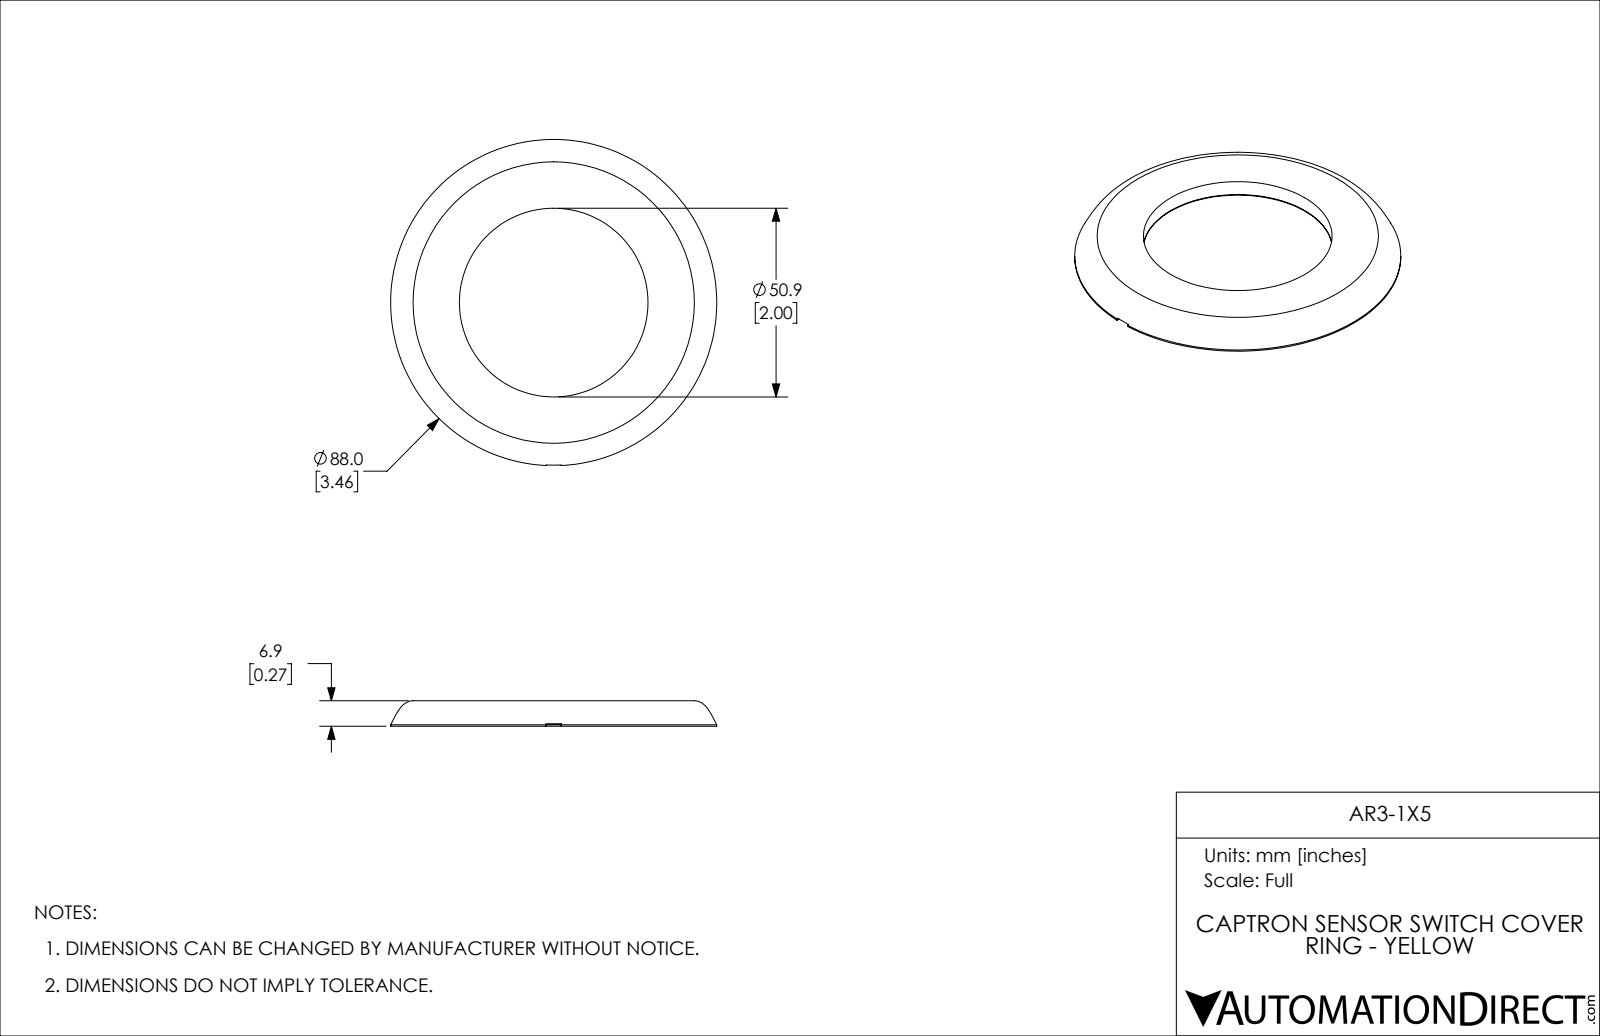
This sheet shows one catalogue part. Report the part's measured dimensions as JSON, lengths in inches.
{"part_name": "AR3-1X5", "step_written_by": "SolidWorks 2019 (CONFIG_CONTROL_DESIGN)", "units": "inches", "bodies": {"solids": 1, "faces": 54, "planar": 12, "cylindrical": 4, "other": 38}, "overall_size": [3.465, 3.463, 0.272], "volume_in3": 0.52, "surface_area_in2": 17.43, "round_holes": [[0.197, 1]], "round_bosses_or_shafts": [[2.177, 1]], "face_to_face_distances": [0.063, 0.122, 0.185, 0.114, 0.177, 0.118, 0.11, 0.067, 0.071, 0.079]}
